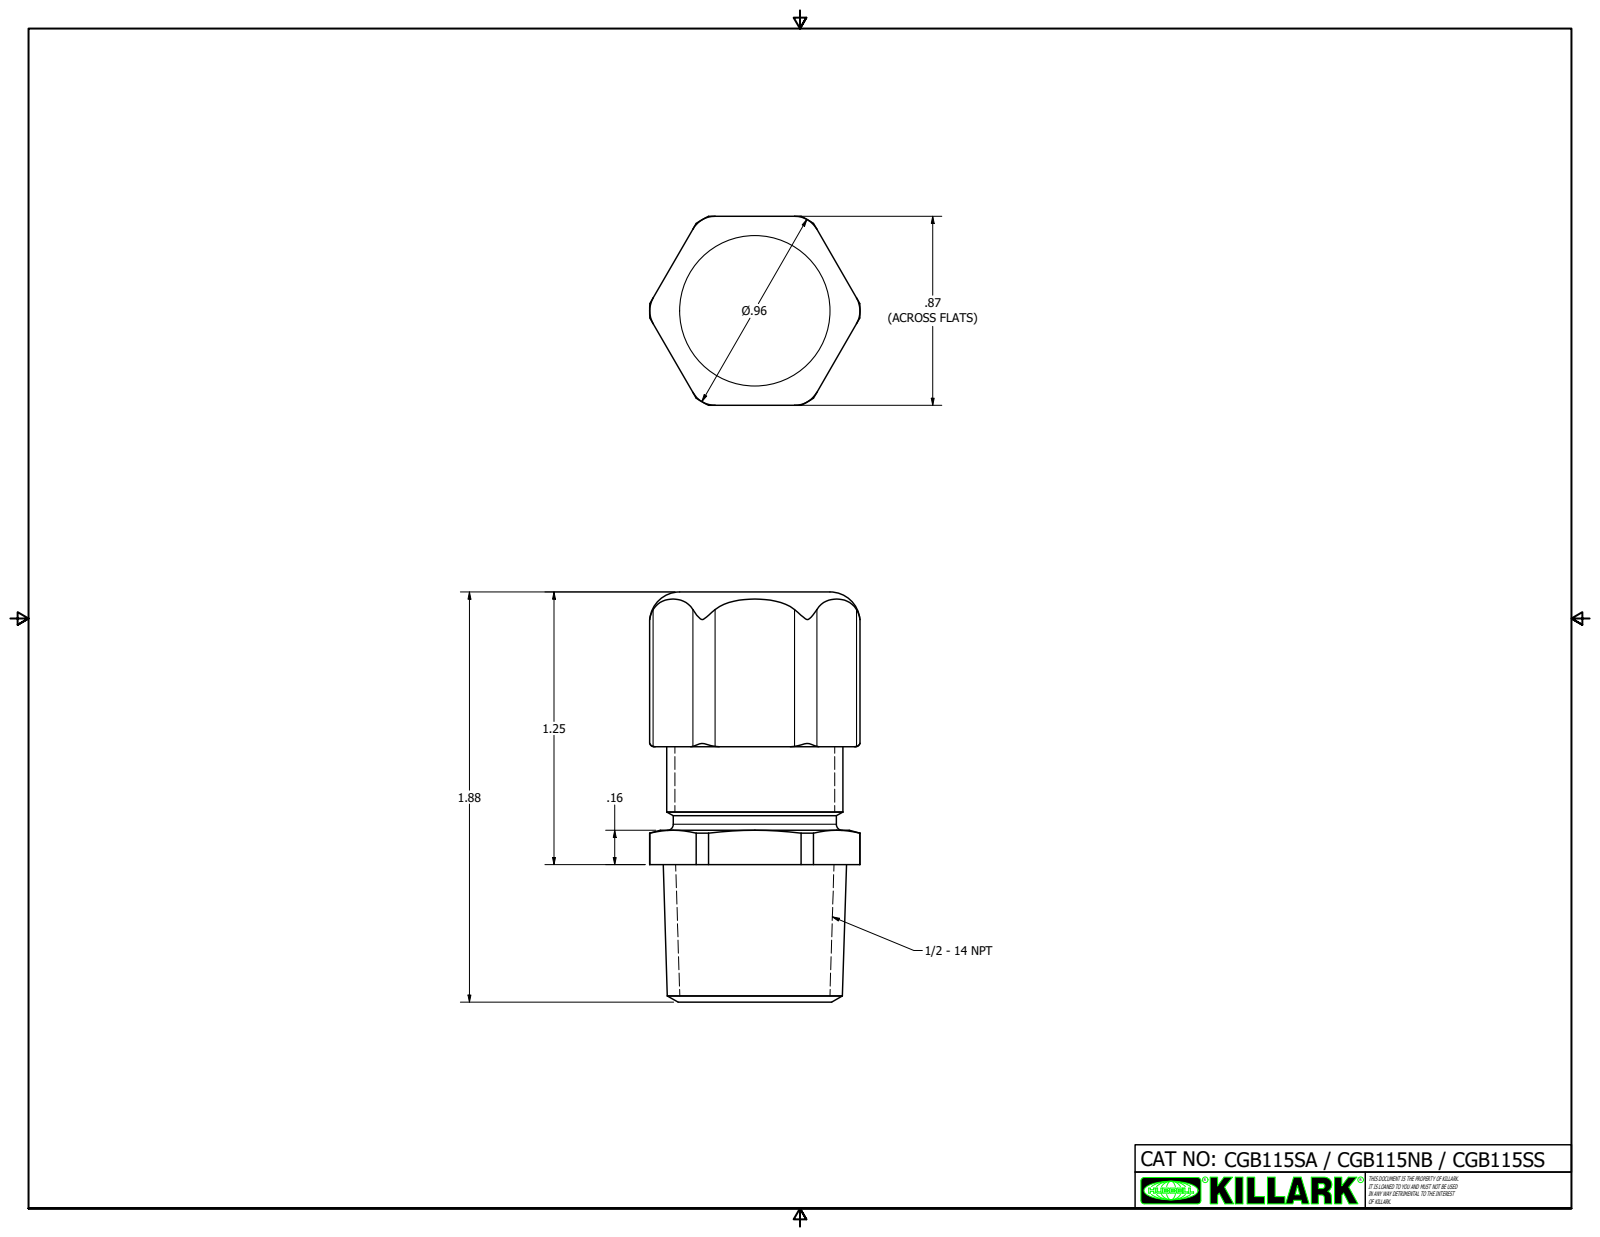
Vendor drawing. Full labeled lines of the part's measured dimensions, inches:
Part name (STEP PRODUCT): CGB115
STEP written by: Autodesk Inventor 2020 (AUTOMOTIVE_DESIGN)
Units: inches
Bodies: 1 solid, 48 faces (17 planar, 14 cylindrical, 17 other)
Overall size (bounding box): 1.879 × 0.965 × 0.866
Volume: 1.076 in³ · Surface area: 6.526 in²
Round bosses / shafts (diameter × count): ⌀0.807 ×1, ⌀0.748 ×1
Partial cylindrical surfaces — rounded edges, fillets, slot ends (radius × count): R0.118 ×6, R0.482 ×1
Main face-to-face distances: 0.866, 1.879, 1.17, 0.709, 0.63, 0.541, 1.249, 0.787, 0.157, 0.383
